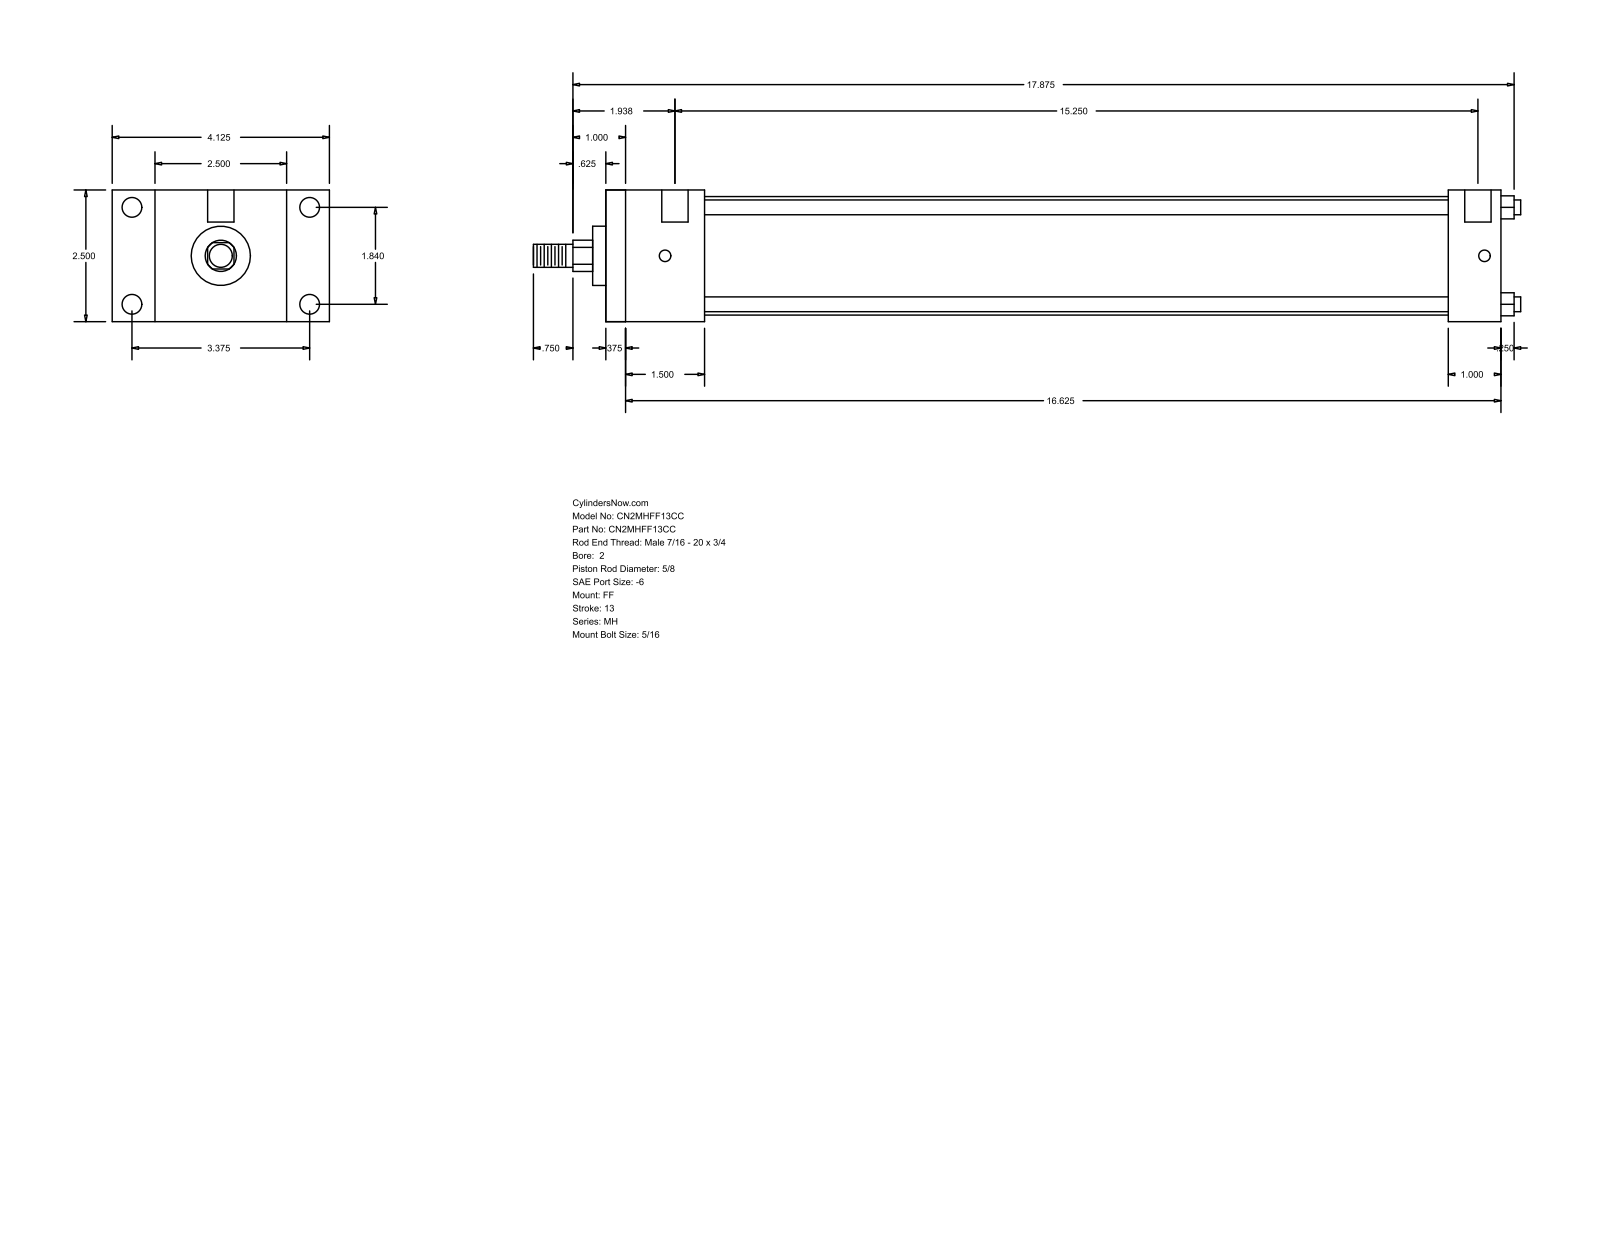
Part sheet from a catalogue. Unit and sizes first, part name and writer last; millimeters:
Units: millimetres
Overall size (bounding box): 476.25 × 104.78 × 63.5
Round holes (diameter × count): ⌀5.56 ×4, ⌀9.53 ×4, ⌀12.7 ×2
Round bosses / shafts (diameter × count): ⌀7.14 ×4, ⌀57.15 ×1, ⌀28.57 ×1, ⌀15.88 ×1, ⌀11.11 ×1
Partial cylindrical surfaces — rounded edges, fillets, slot ends (radius × count): R7.54 ×1
Main face-to-face distances: 63.5, 431.8, 9.52, 422.28, 38.1, 47.62, 406.39, 396.87, 358.77, 384.18
Hole centre spacings: 46.74, 85.72, 97.63, 395.29, 3.18, 4.76, 387.35, 390.53
Bodies: 0 solids, 92 faces (64 planar, 28 cylindrical, 0 other)
Part name (STEP PRODUCT): MH_FF__0200_0.625
STEP written by: GSSL Pune (CONFIG_CONTROL_DESIGN)
